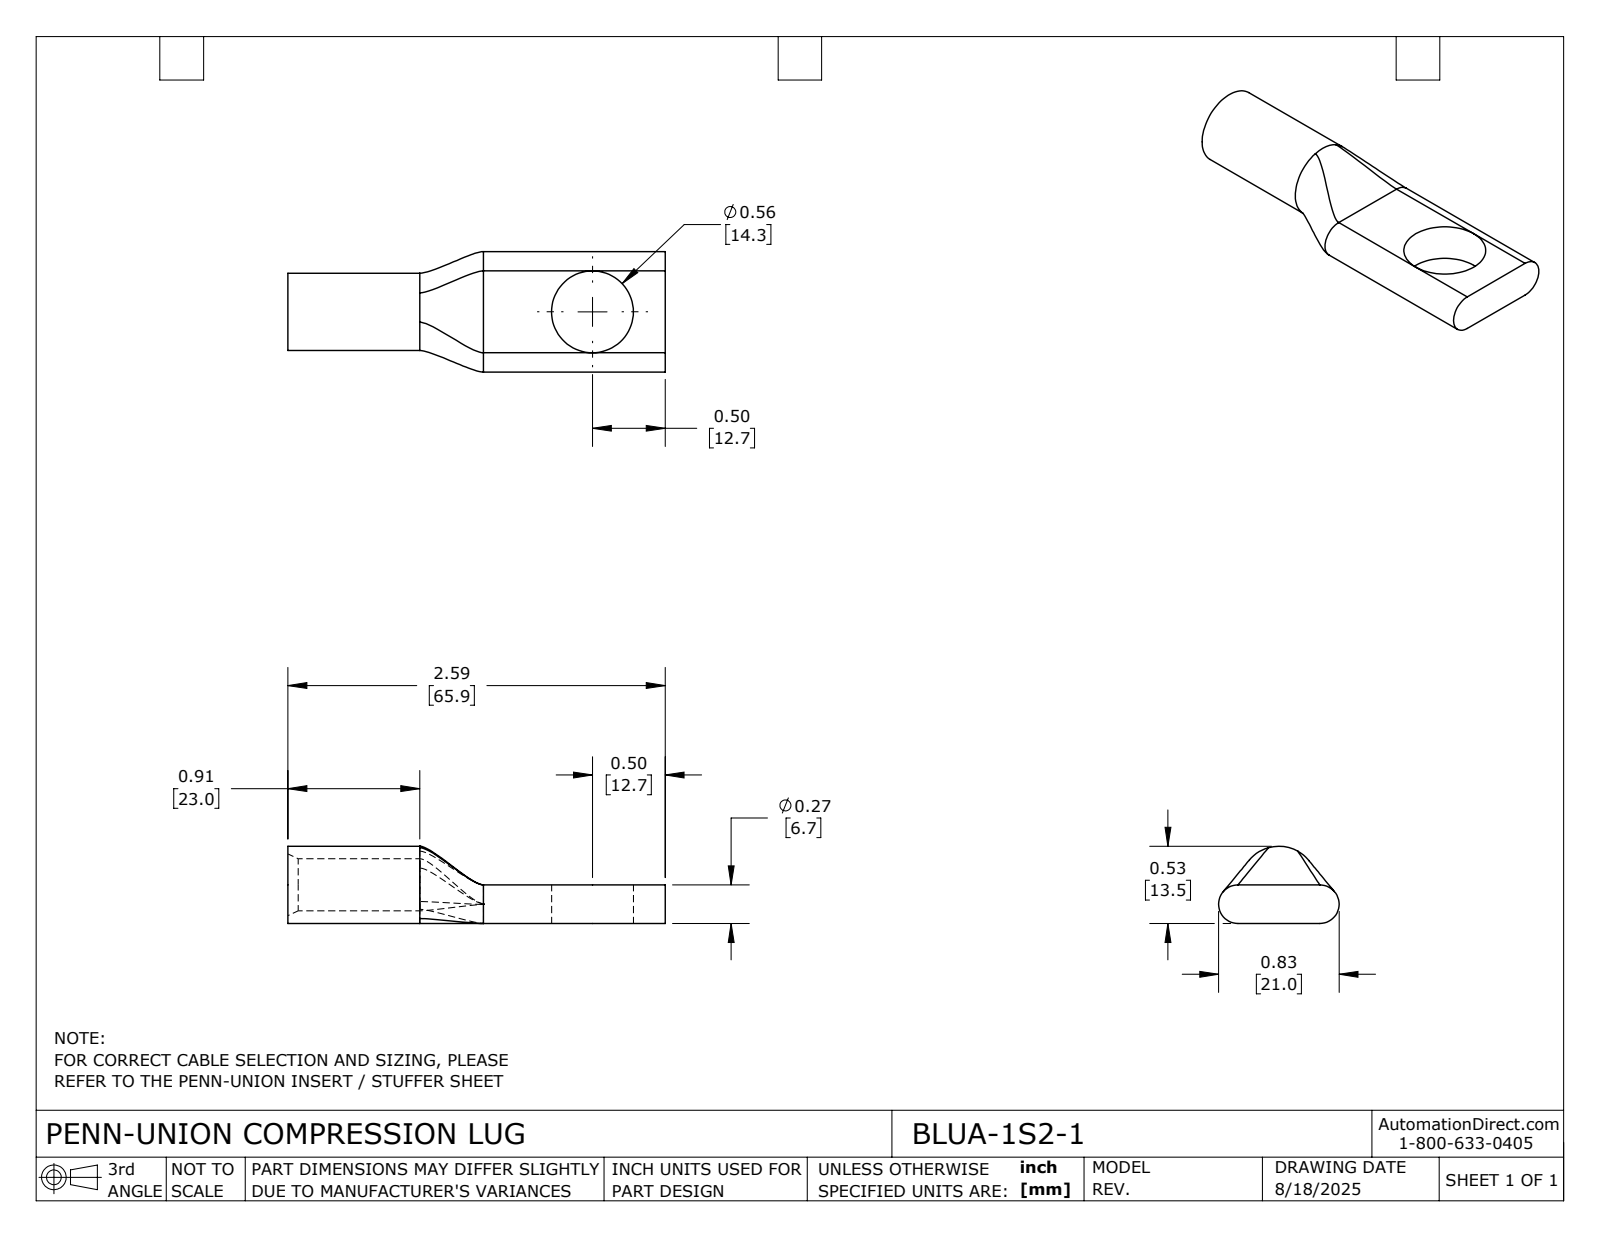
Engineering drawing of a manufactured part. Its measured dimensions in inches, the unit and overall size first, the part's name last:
Units: inches
Overall size (bounding box): 2.594 × 0.828 × 0.531
Round holes (diameter × count): ⌀0.358 ×1, ⌀0.563 ×1
Round bosses / shafts (diameter × count): ⌀0.531 ×1
Partial cylindrical surfaces — rounded edges, fillets, slot ends (radius × count): R0.133 ×2
Main face-to-face distances: 0.266, 2.594, 1.344, 1.25
Volume: 0.368 in³ · Surface area: 6.619 in²
Bodies: 1 solid, 26 faces (7 planar, 9 cylindrical, 10 other)
Part name (STEP PRODUCT): BLUA-1S2-1
STEP written by: SolidWorks 2024 (CONFIG_CONTROL_DESIGN)
